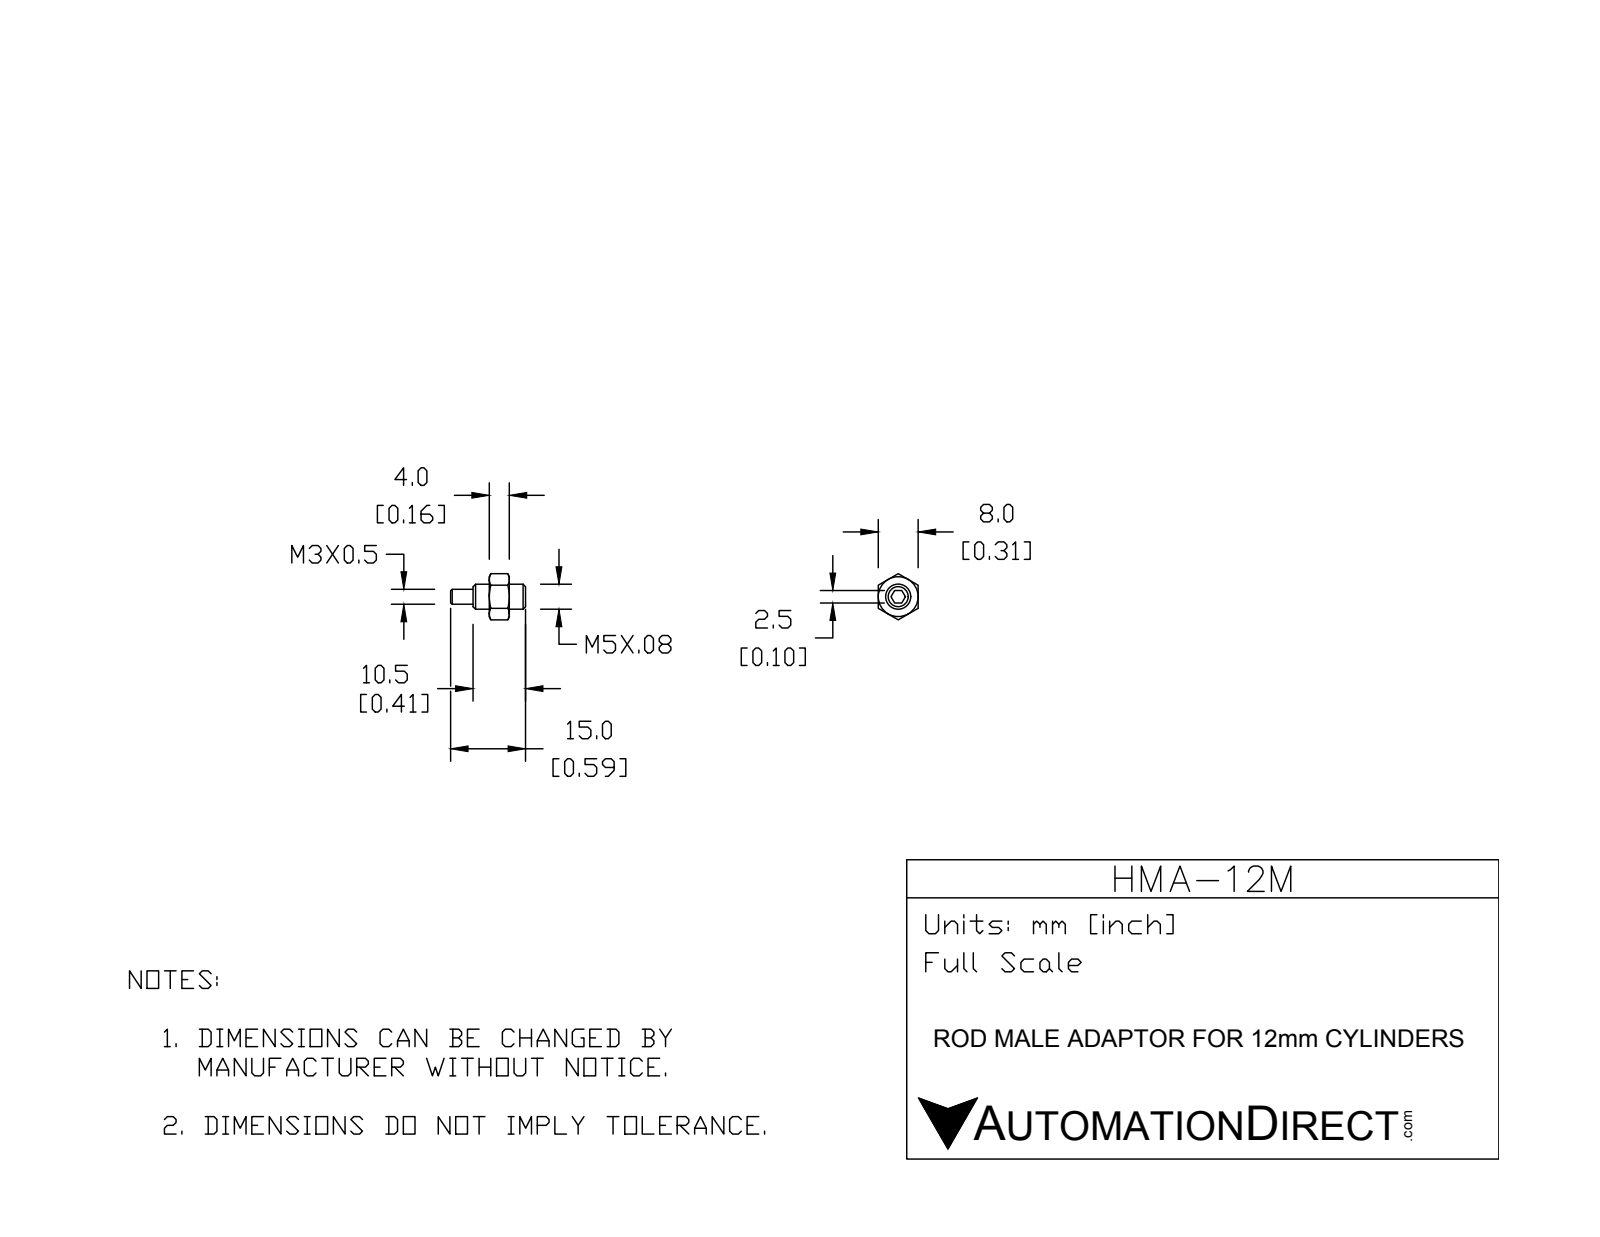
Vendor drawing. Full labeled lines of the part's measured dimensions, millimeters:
Part name (STEP PRODUCT): HMA-12M
STEP written by: SolidWorks 2015 (CONFIG_CONTROL_DESIGN)
Units: millimetres
Bodies: 2 solids, 44 faces (18 planar, 6 cylindrical, 20 other)
Overall size (bounding box): 15 × 9.24 × 8
Volume: 360 mm³ · Surface area: 502 mm²
Round holes (diameter × count): ⌀5 ×1
Round bosses / shafts (diameter × count): ⌀3 ×1
Main face-to-face distances: 8, 4, 2.5, 3.25, 7.25, 10.5, 3, 4.25, 7.5, 15
